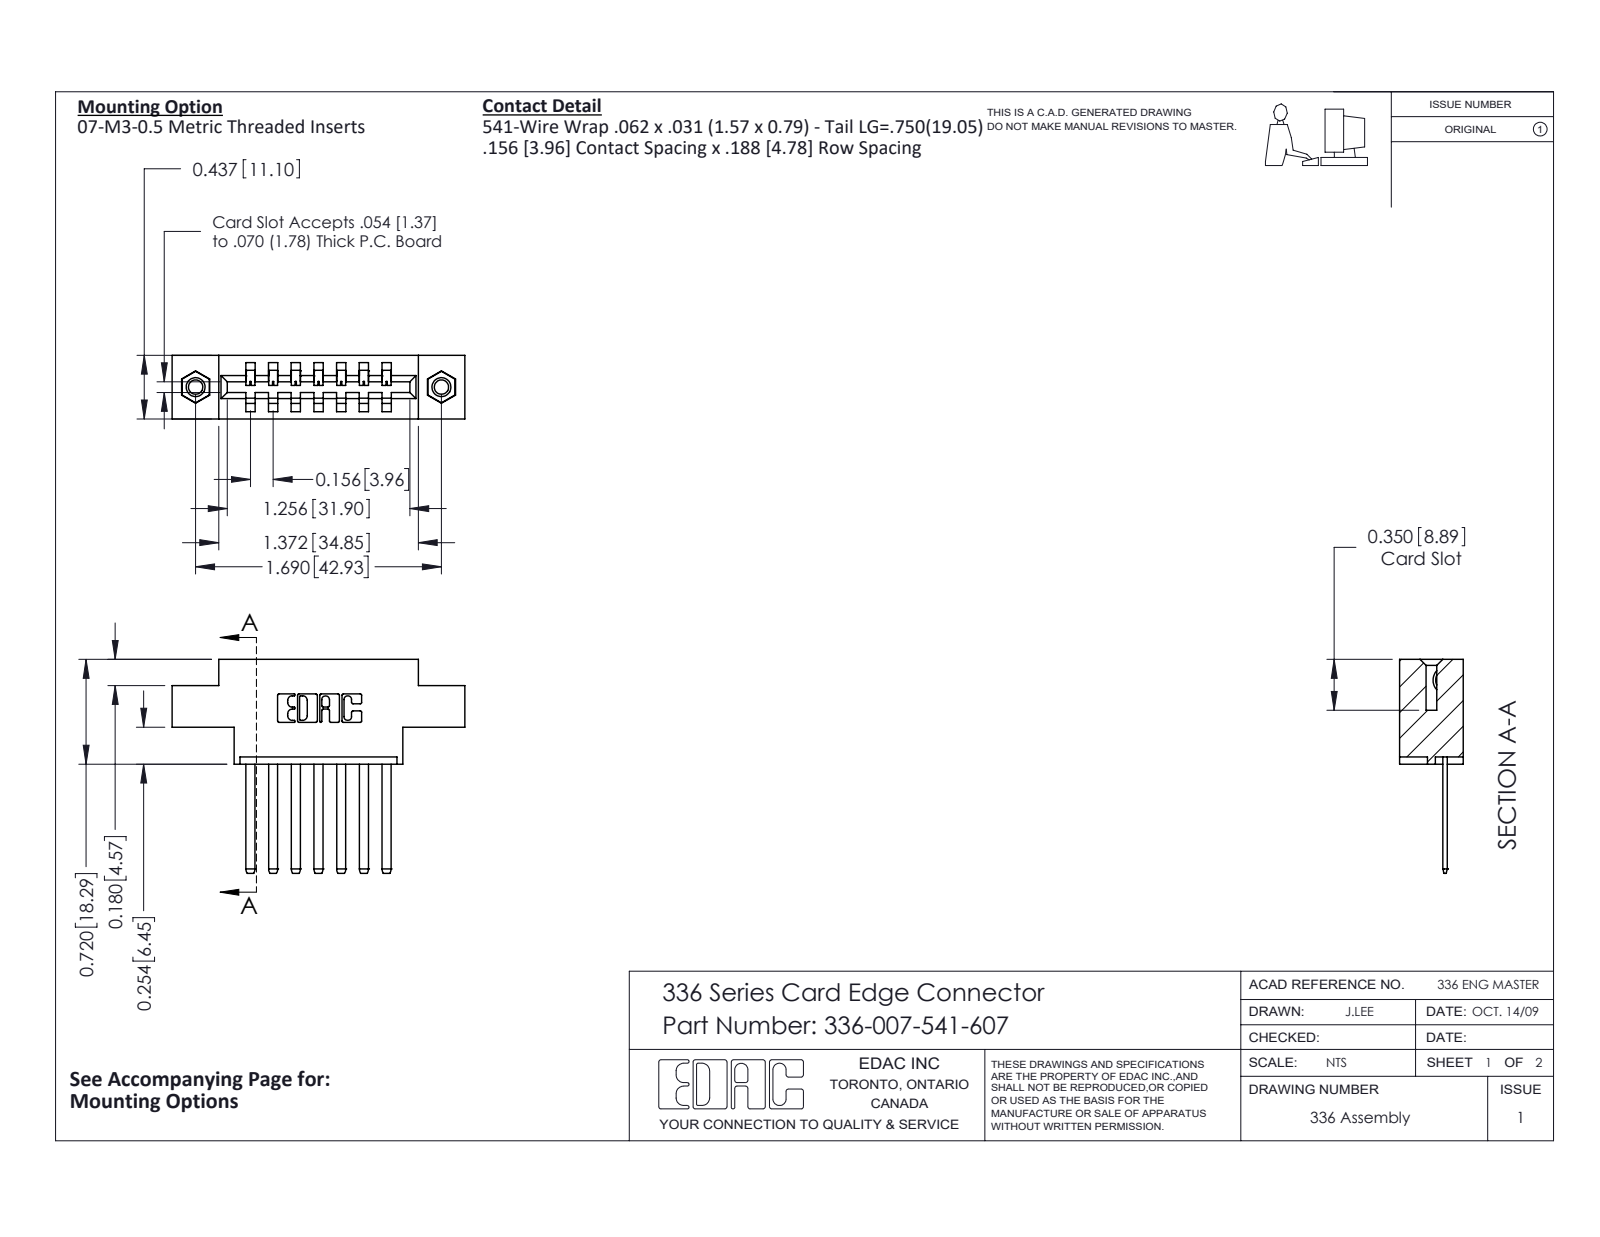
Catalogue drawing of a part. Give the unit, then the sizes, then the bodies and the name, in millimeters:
Units: millimetres
Overall size (bounding box): 51.1 × 37.3 × 11.1
Round holes (diameter × count): ⌀2.5 ×2, ⌀3.2 ×2, ⌀4 ×2
Round bosses / shafts (diameter × count): ⌀3.9 ×2
Partial cylindrical surfaces — rounded edges, fillets, slot ends (radius × count): R0.3 ×22, R0.1 ×14, R1.4 ×14, R0.2 ×6, R0.8 ×6, R0.7 ×3, R0.6 ×2, R1 ×2
Main face-to-face distances: 4, 11.1, 7.9, 5.6, 7.9, 11.9, 15.8, 4.6, 6.5, 6.3
Hole centre spacings: 42.9
Volume: 6 420 mm³ · Surface area: 6 665 mm²
Bodies: 10 solids, 528 faces (344 planar, 168 cylindrical, 16 other)
Part name (STEP PRODUCT): 336-290-001_336-290-541; 336-007-541-607; 336 Part_Offset - .156 Dia - TI; 345-250-001_345-250-005-103
STEP written by: SolidWorks 2020 (CONFIG_CONTROL_DESIGN)
